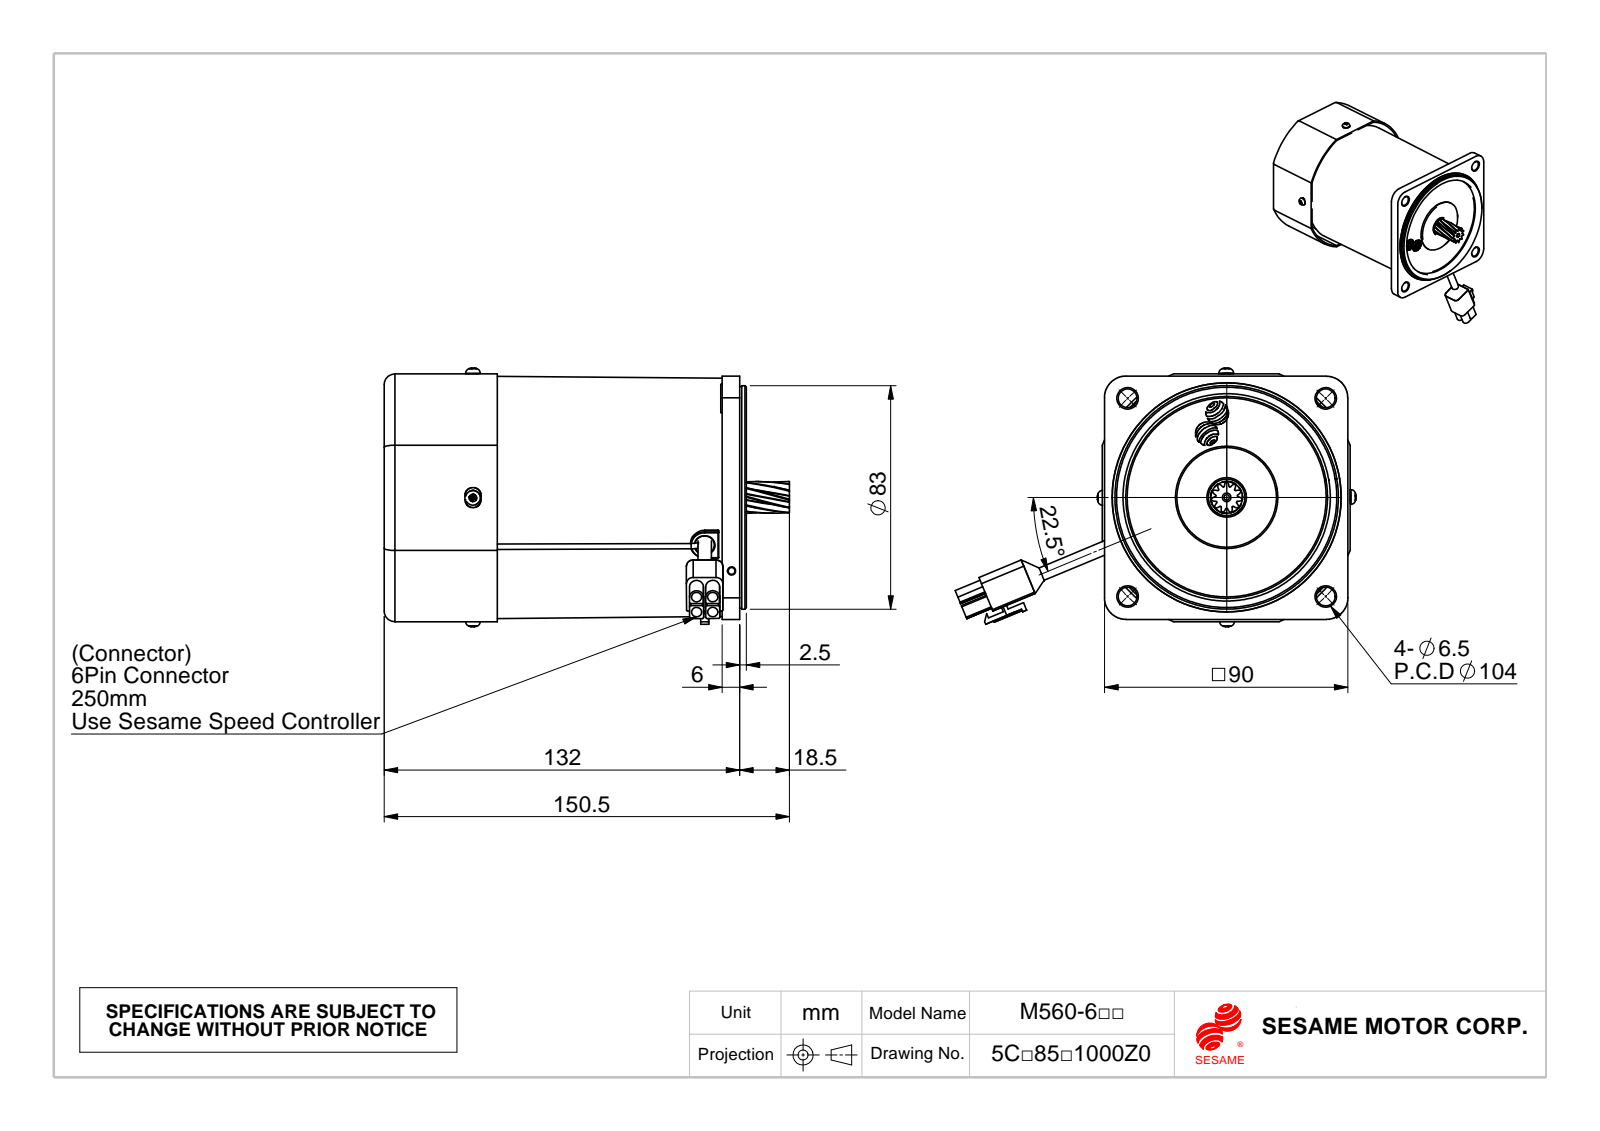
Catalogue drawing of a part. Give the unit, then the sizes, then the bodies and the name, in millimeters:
Units: millimetres
Overall size (bounding box): 150.5 × 148.74 × 95.89
Round holes (diameter × count): ⌀2.5 ×7, ⌀3.8 ×4, ⌀5.5 ×4, ⌀7 ×4, ⌀2 ×2, ⌀3.1 ×2, ⌀24 ×2, ⌀6.5 ×1, ⌀7.2 ×1, ⌀9.5 ×1, ⌀10 ×1, ⌀13.7 ×1
Round bosses / shafts (diameter × count): ⌀5.5 ×4, ⌀3 ×4, ⌀47 ×2, ⌀2 ×2, ⌀84.22 ×1, ⌀83 ×1, ⌀82.2 ×1, ⌀58 ×1
Partial cylindrical surfaces — rounded edges, fillets, slot ends (radius × count): R0.3 ×16, R0.5 ×14, R1 ×14, R0.25 ×8, R0.78 ×8, R1.5 ×8, R1.66 ×8, R2.92 ×8
Main face-to-face distances: 1, 27, 91, 129.4, 130.4, 28, 102.4, 123.1, 122.1, 95.1
Hole centre spacings: 6, 52, 4.24, 5.01, 3.6, 38.18, 73.18, 73.54
Volume: 741 013 mm³ · Surface area: 118 080 mm²
Bodies: 13 solids, 911 faces (293 planar, 425 cylindrical, 193 other)
Part name (STEP PRODUCT): 風扇蓋FC-9042-33; 油封10x26x5; 公端子; M560-R-F (+2 more)
STEP written by: SolidWorks 2010 (CONFIG_CONTROL_DESIGN)
